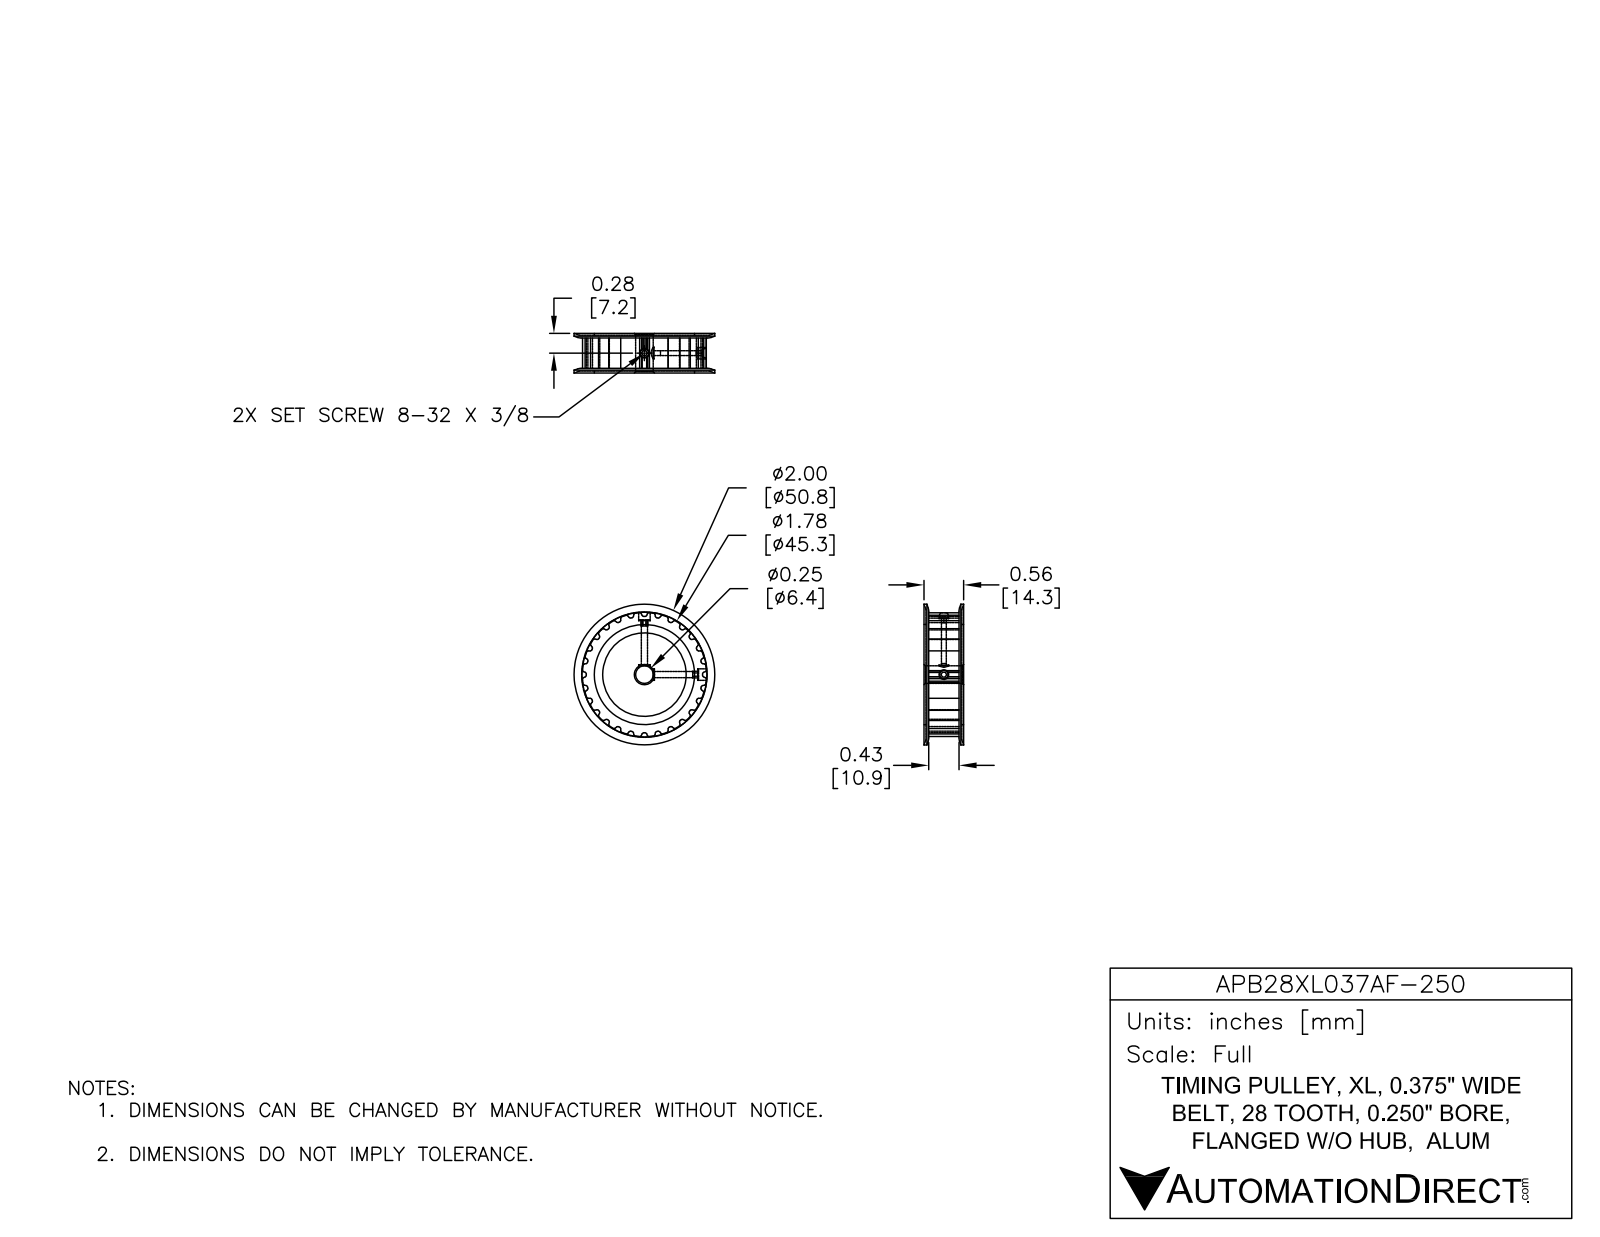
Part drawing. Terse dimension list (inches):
name: APB28XL037AF-250
written by: SolidWorks 2014 (AUTOMOTIVE_DESIGN)
unit: in
bodies: 1 solid, 293 faces (96 planar, 173 cylindrical, 24 other)
size: 2 × 2 × 0.558
volume: 1.226 in³; area: 12.47 in²
holes: 2× ⌀0.127, 1× ⌀0.25
bosses: 1× ⌀1.188
rounds: 112× R0.015, 1× R0.826
face distances: 0.495, 0.033, 0.528, 0.557, 0.525, 0.03, 1.763, 0.654, 0.462, 0.063
